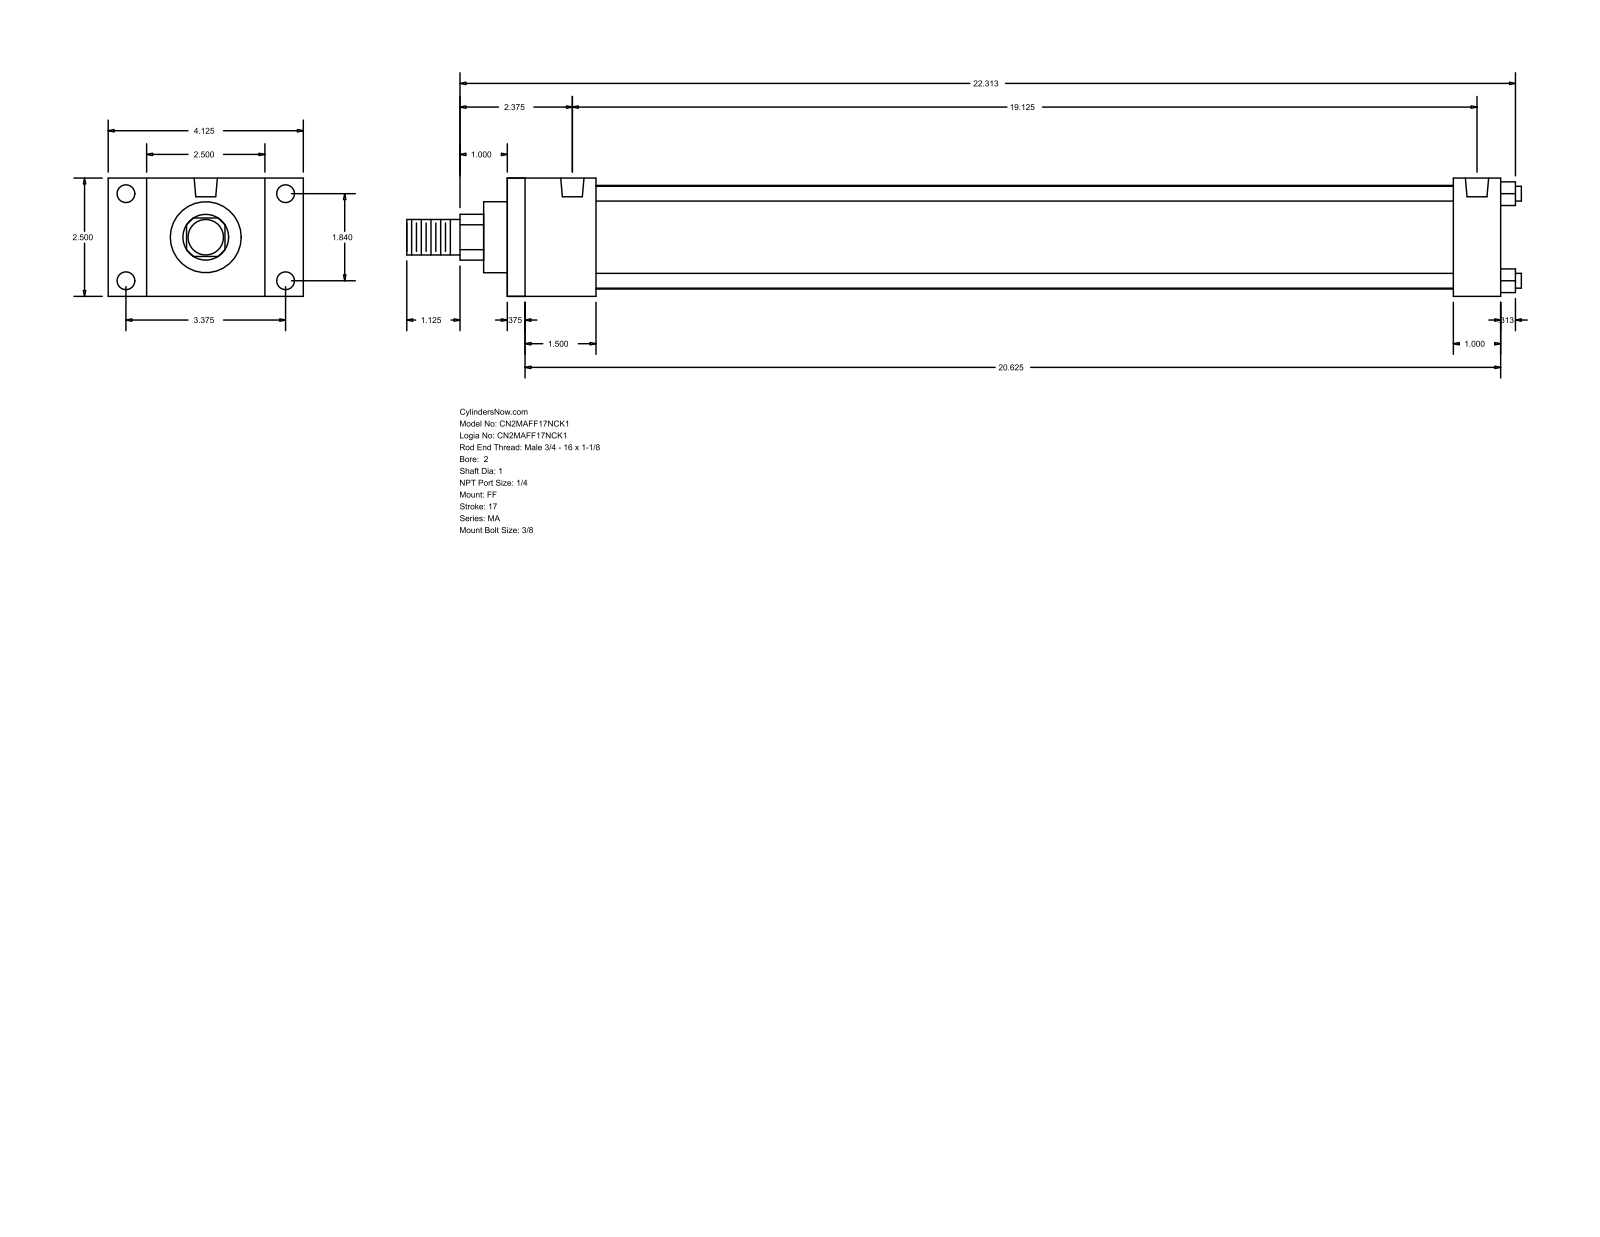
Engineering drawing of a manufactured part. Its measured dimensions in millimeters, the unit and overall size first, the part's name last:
Units: millimetres
Overall size (bounding box): 598.49 × 104.78 × 63.5
Round holes (diameter × count): ⌀7.94 ×4, ⌀9.53 ×4, ⌀12.49 ×2
Round bosses / shafts (diameter × count): ⌀7.94 ×4, ⌀55.63 ×1, ⌀38.1 ×1, ⌀25.4 ×1, ⌀19.05 ×1
Partial cylindrical surfaces — rounded edges, fillets, slot ends (radius × count): R12.29 ×1
Main face-to-face distances: 63.5, 533.4, 9.52, 523.88, 25.4, 20.64, 12.7, 47.63, 508, 38.11
Hole centre spacings: 46.74, 85.72, 97.63, 485.77
Bodies: 0 solids, 92 faces (64 planar, 28 cylindrical, 0 other)
Part name (STEP PRODUCT): MA_FF__0200_1
STEP written by: GSSL Pune (CONFIG_CONTROL_DESIGN)
